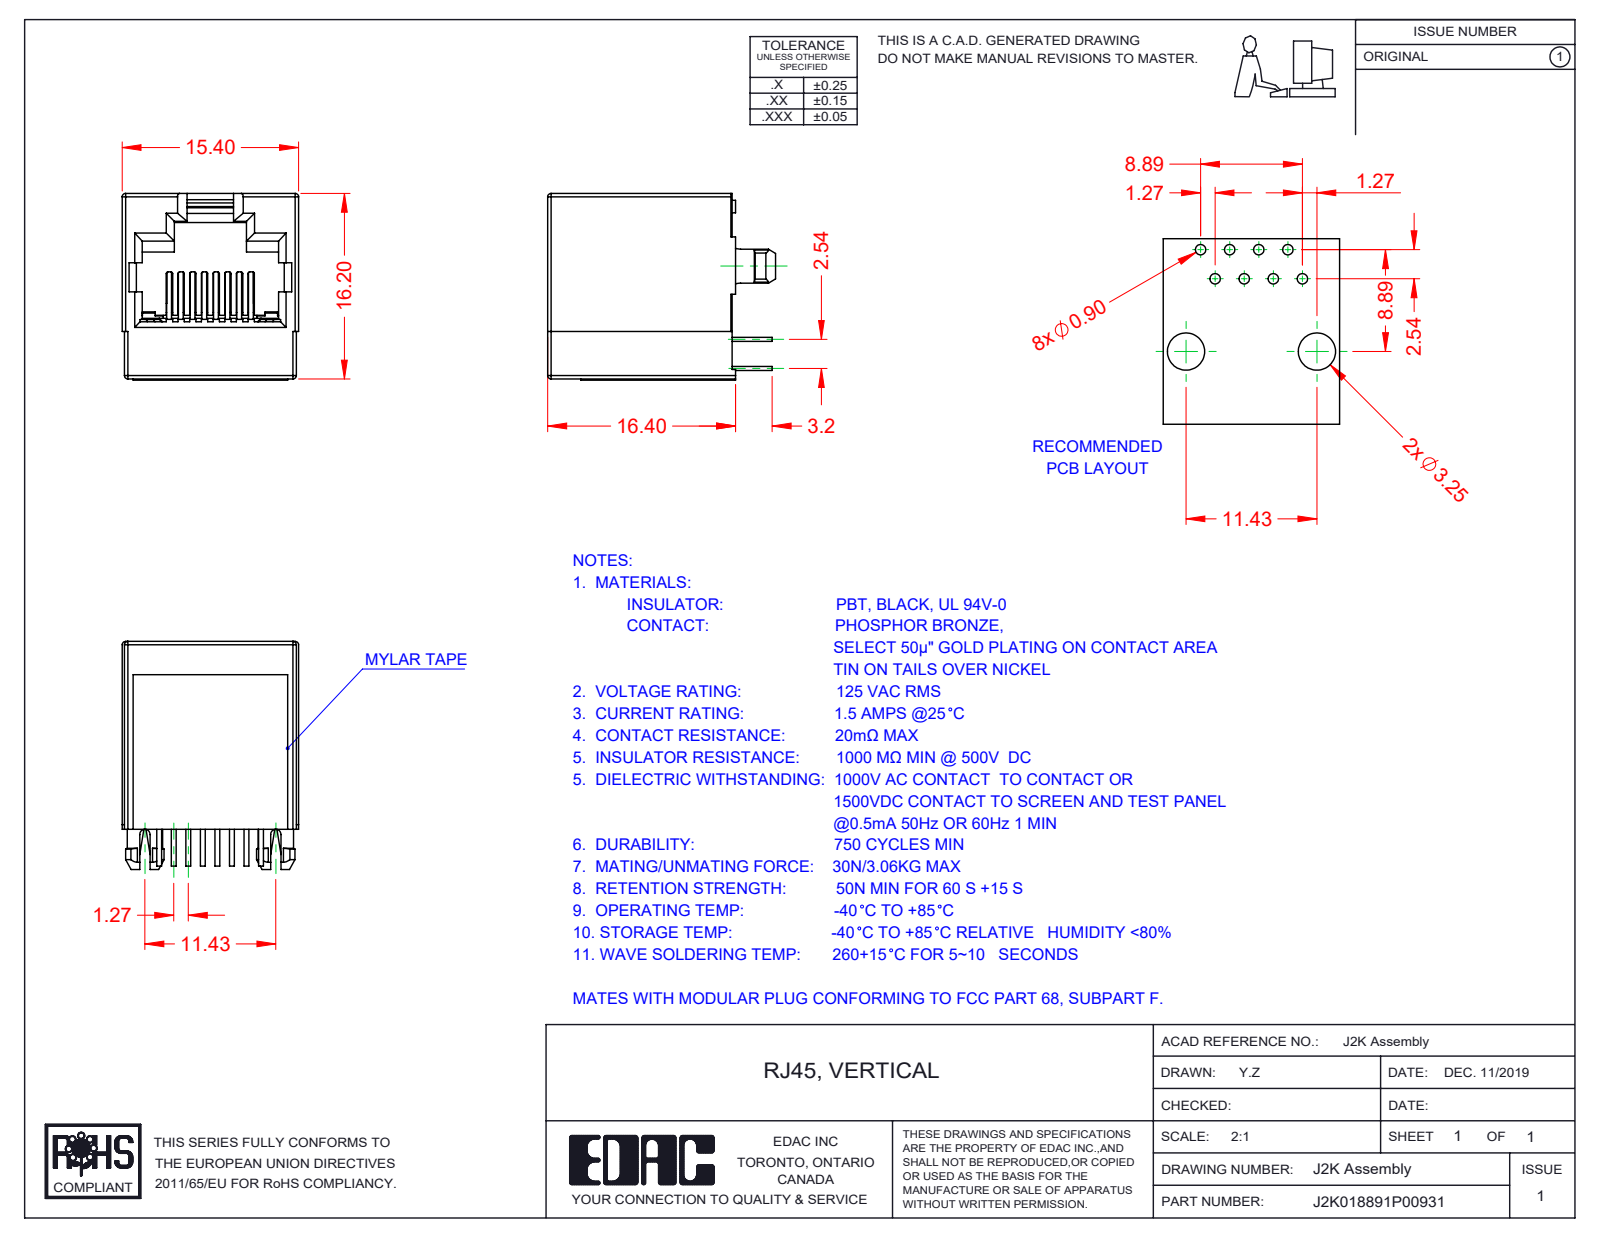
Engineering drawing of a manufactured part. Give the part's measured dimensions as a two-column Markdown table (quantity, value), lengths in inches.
| quantity | value |
| --- | --- |
| part name | RJ2K018891P00931; 2K Contacts; 2K Insulator; 2K Contact Lock (+1 more) |
| STEP written by | SolidWorks 2016 (CONFIG_CONTROL_DESIGN) |
| units | inches |
| bodies | 11 solids, 729 faces (592 planar, 113 cylindrical, 24 other) |
| overall size | 0.783 × 0.642 × 0.606 |
| volume | 0.152 in³ |
| surface area | 6.715 in² |
| round bosses / shafts (diameter × count) | 0.122 × 2, 0.043 × 2 |
| partial cylindrical surfaces (radius × count) | 0.006 × 16, 0.012 × 10, 0.02 × 3, 0.004 × 2, 0.008 × 2, 0.018 × 2, 0.024 × 2, 0.037 × 2 |
| main face-to-face distances | 0.638, 0.606, 0.642, 0.551, 0.055, 0.047, 0.543, 0.598, 0.02, 0.051 |
